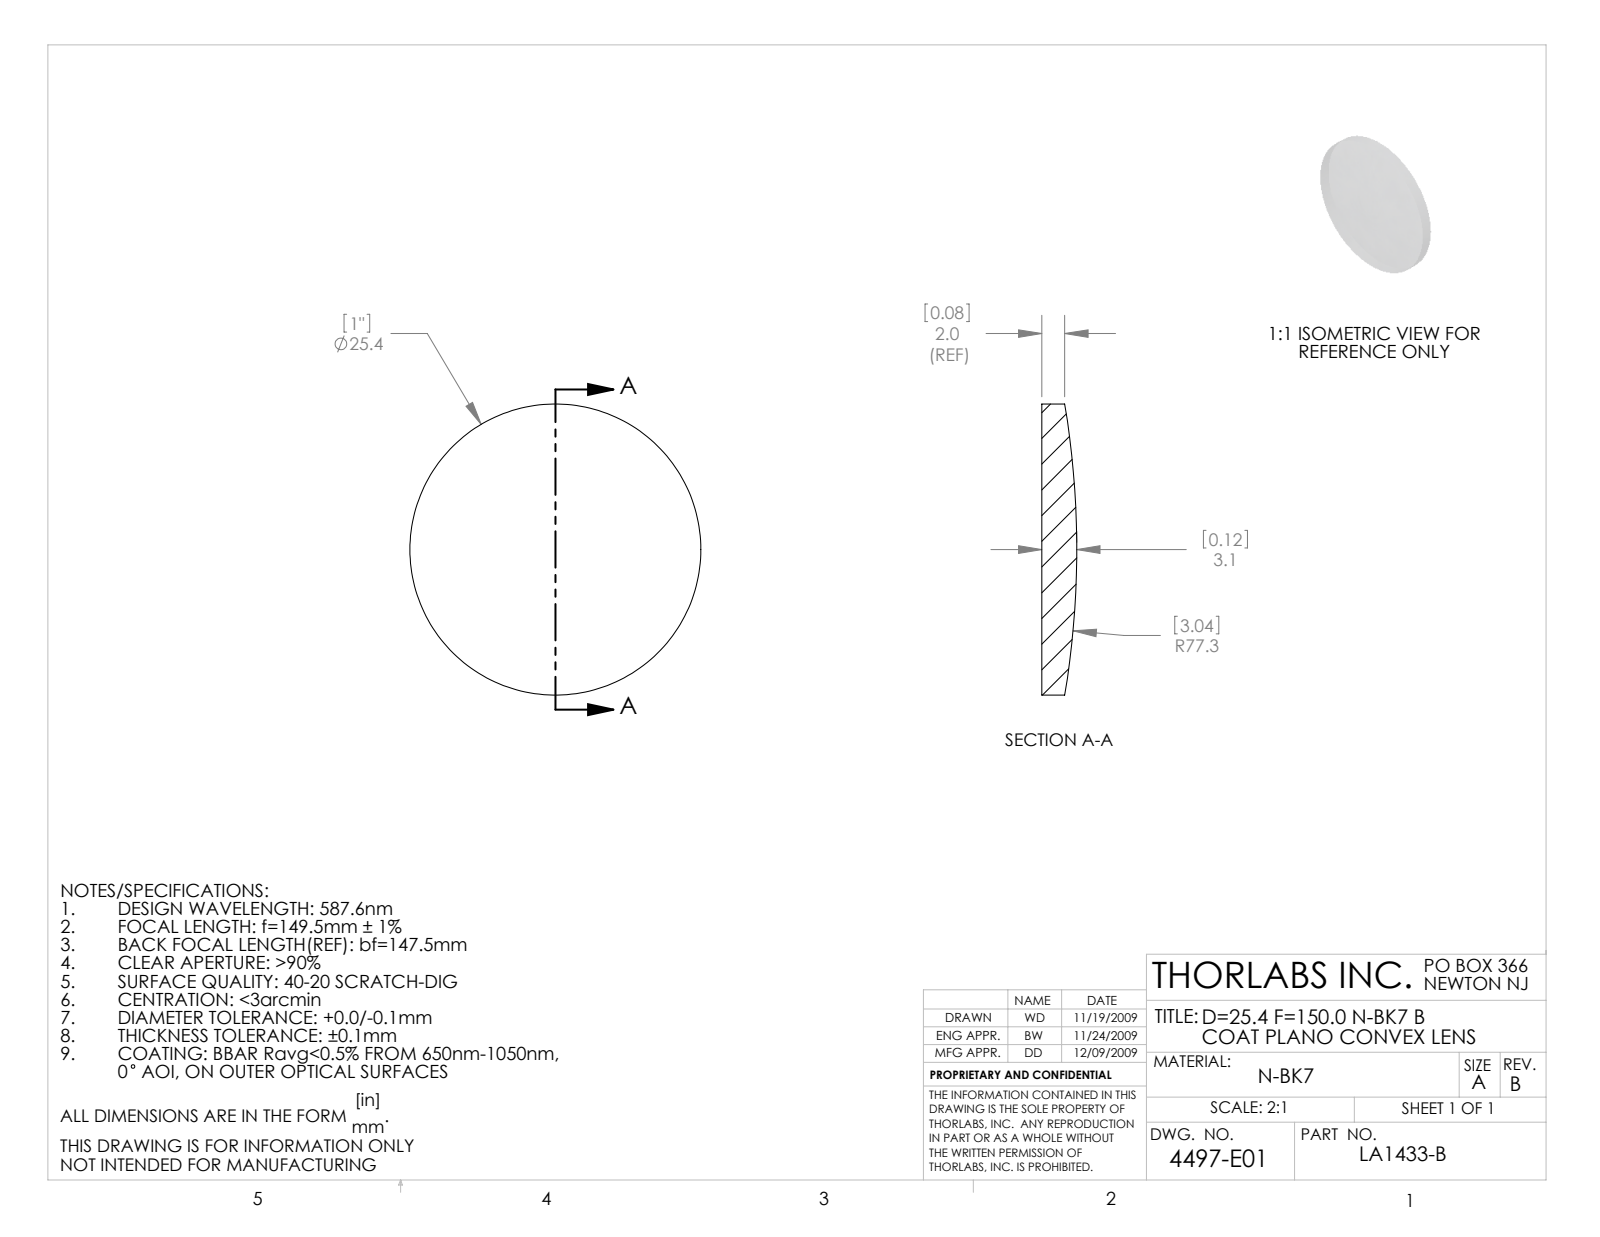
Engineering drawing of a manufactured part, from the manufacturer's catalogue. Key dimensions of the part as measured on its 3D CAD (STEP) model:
Part name (STEP PRODUCT): 4497-E0W
STEP written by: SolidWorks 2009 (AUTOMOTIVE_DESIGN)
Units: millimetres
Bodies: 1 solid, 5 faces (1 planar, 2 cylindrical, 2 other)
Overall size (bounding box): 25.4 × 25.4 × 3.05
Volume: 1 280 mm³ · Surface area: 1 176 mm²
Round bosses / shafts (diameter × count): ⌀25.4 ×1
